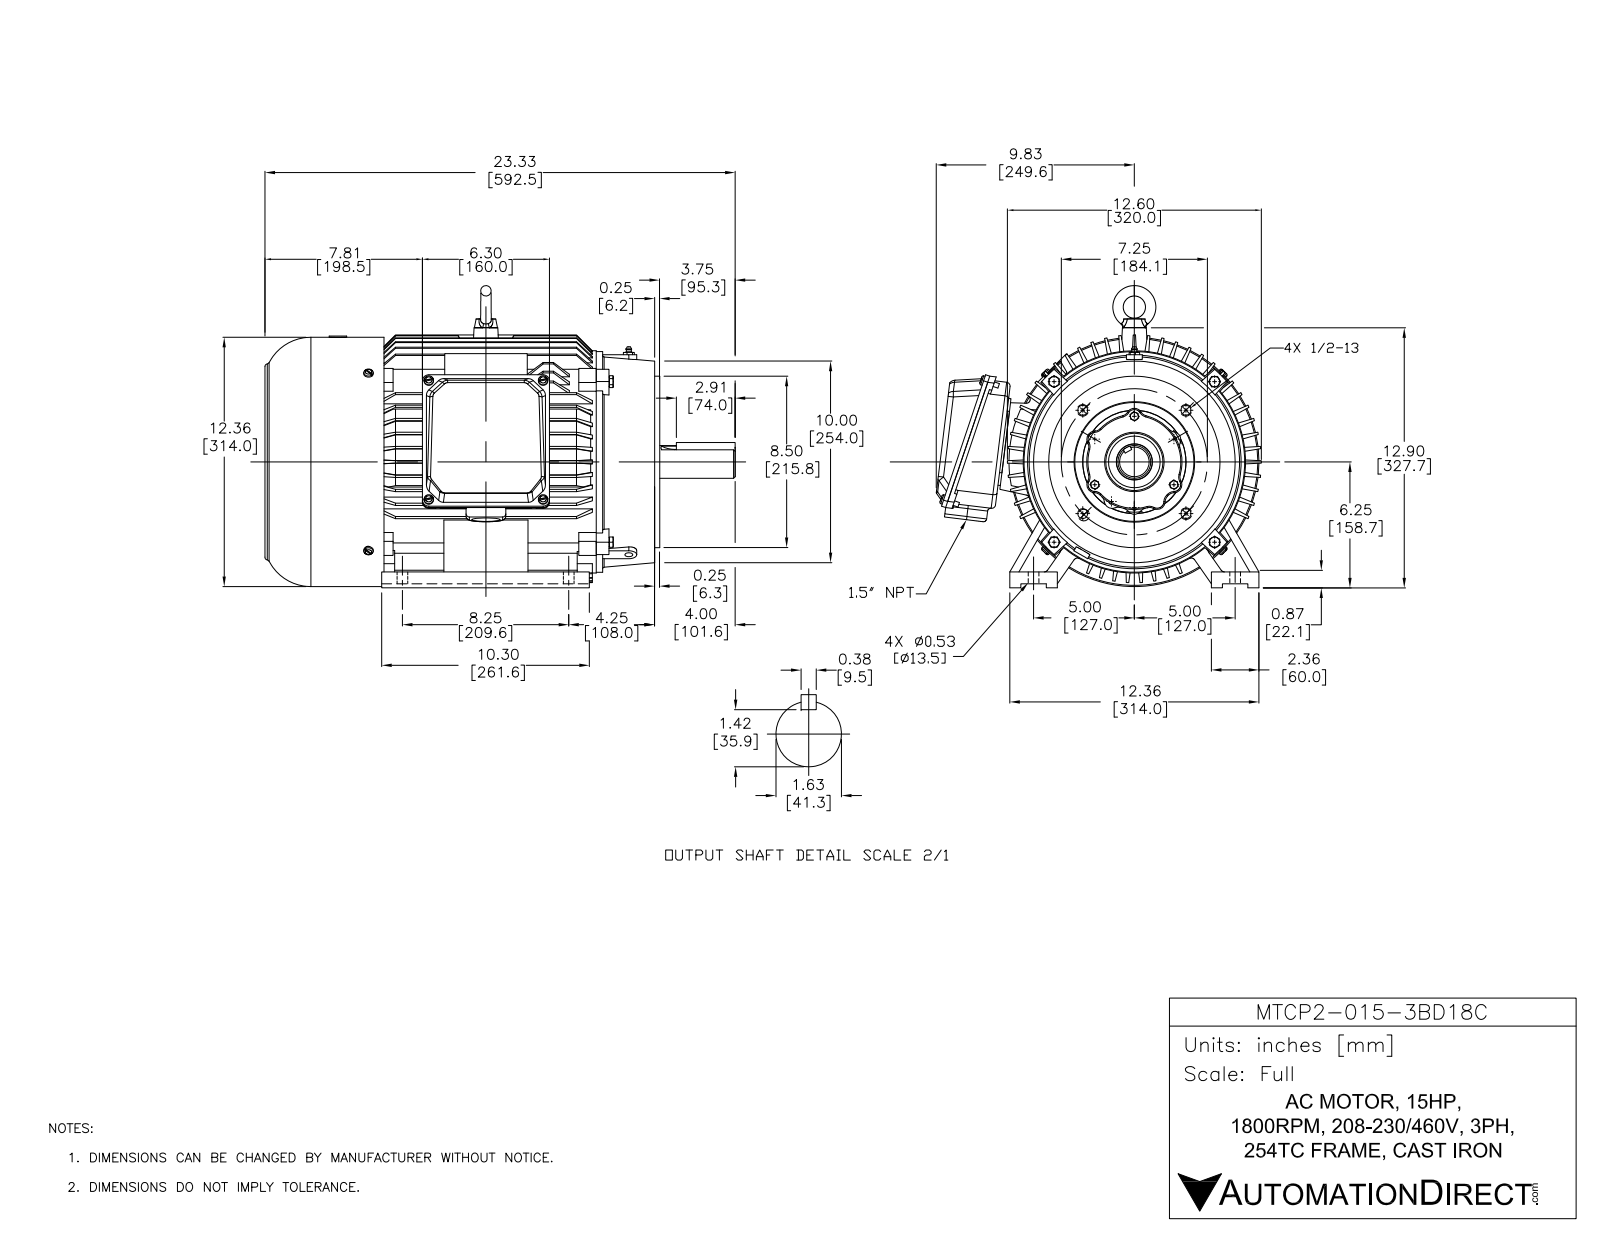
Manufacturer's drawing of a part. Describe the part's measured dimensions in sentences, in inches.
The part is named "PEWWE-254TC". Its 3-D file was written by "SolidWorks 2017 (AUTOMOTIVE_DESIGN)". It is 28 solids with 2201 faces: 1371 planar, 429 cylindrical and 401 other. Overall it measures 23.327 by 16.126 by 14.984 inches. Its volume is 490.4 cubic inches and its surface area 3 124 square inches. Round holes: 13 of diameter 0.276, 10 of diameter 0.236, 8 of diameter 0.315, 8 of diameter 0.394, 4 of diameter 0.197, 4 of diameter 0.492, 4 of diameter 0.551, 2 of diameter 0.748, 1 of diameter 0.079, 1 of diameter 0.472, 1 of diameter 1.417, 1 of diameter 1.791. Round bosses or shafts: 8 of diameter 0.236, 1 of diameter 12.362, 1 of diameter 11.024, 1 of diameter 10.945, 1 of diameter 10.928, 1 of diameter 10.354, 1 of diameter 8.5, 1 of diameter 2.953. Partial cylindrical surfaces (rounded edges, fillets, slot ends): 50 of radius 0.394, 30 of radius 0.157, 14 of radius 0.197, 8 of radius 0.315, 7 of radius 0.138, 4 of radius 0.63, 2 of radius 0.004, 2 of radius 0.118. The main face-to-face distances are 0.197, 0.059, 2.52, 0.787, 17.807, 17.866, 10.945, 2.796, 1.662, 19.469. The hole center spacings are 2.953, 2.264, 6.694, 3.921, 4.176, 4.742, 5.498, 5.838.
